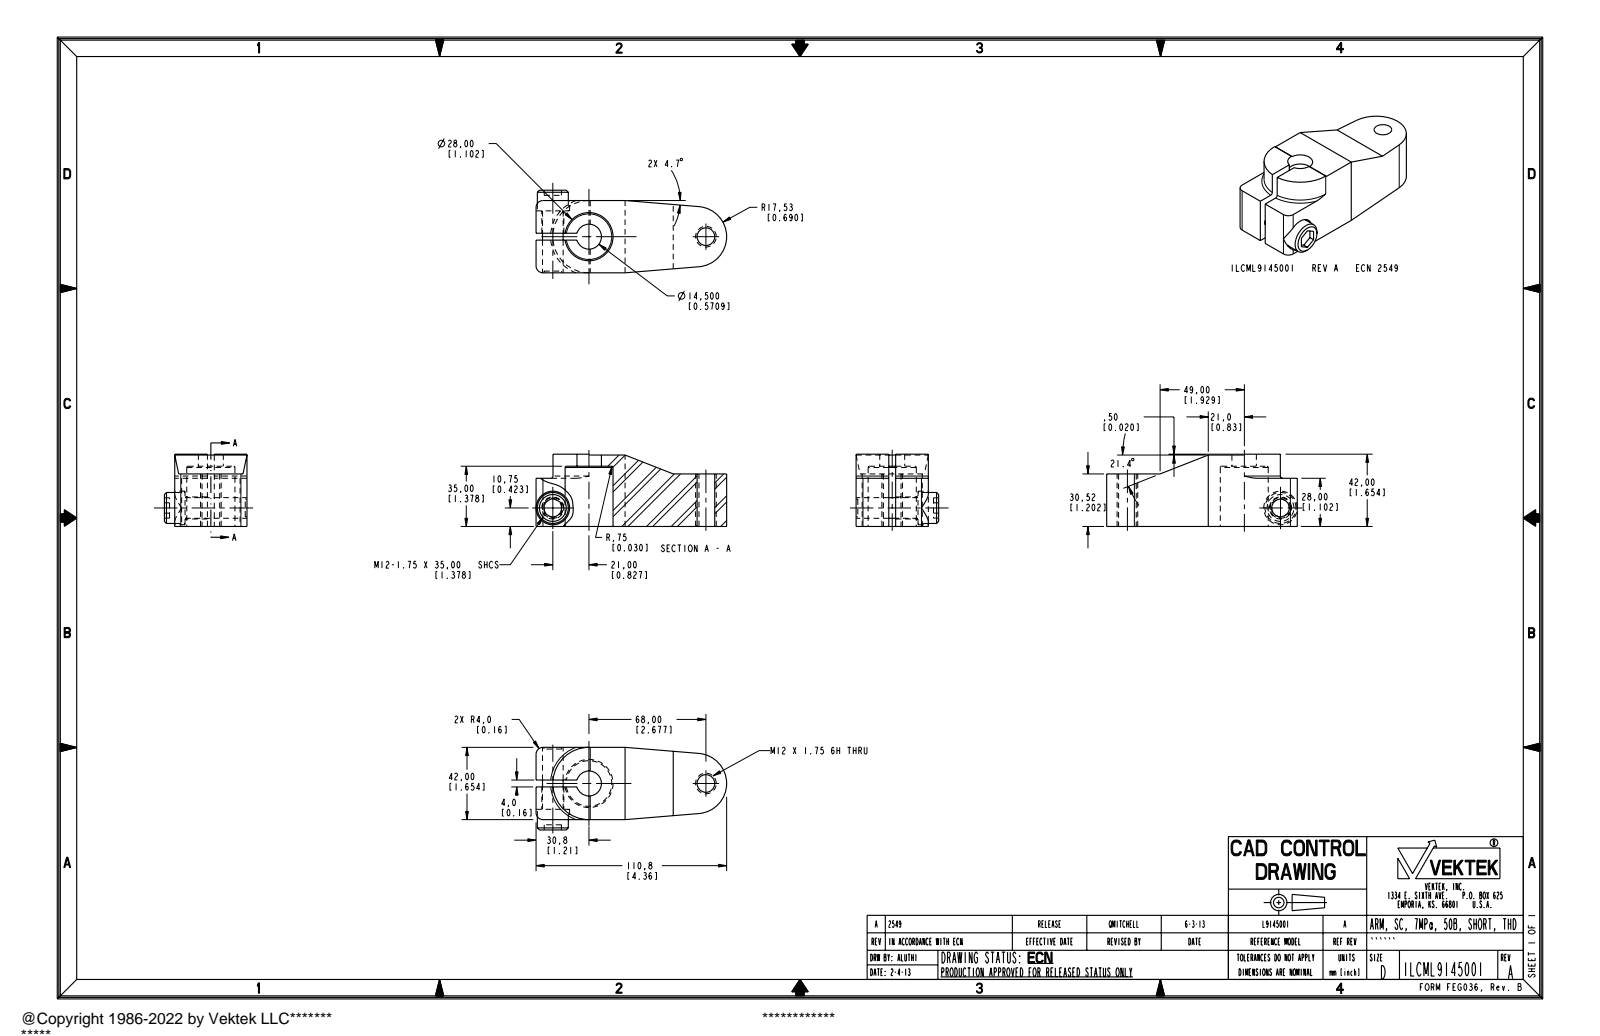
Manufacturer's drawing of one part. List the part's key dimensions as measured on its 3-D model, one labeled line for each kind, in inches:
Part name (STEP PRODUCT): ILCML9145001
STEP written by: PRO/ENGINEER BY PARAMETRIC TECHNOLOGY CORPORATION, 2007460 (AUTOMOTIVE_DESIGN_CC2)
Units: inches
Bodies: 1 solid, 59 faces (28 planar, 26 cylindrical, 5 other)
Overall size (bounding box): 4.362 × 1.89 × 1.654
Volume: 7.668 in³ · Surface area: 41.9 in²
Round holes (diameter × count): ⌀0.404 ×2, ⌀0.504 ×1, ⌀0.571 ×1, ⌀0.768 ×1, ⌀1.102 ×1
Round bosses / shafts (diameter × count): ⌀0.472 ×2, ⌀0.709 ×1
Partial cylindrical surfaces — rounded edges, fillets, slot ends (radius × count): R0.157 ×2, R0.031 ×1, R0.69 ×1, R0.827 ×1
Main face-to-face distances: 1.654, 0.748, 0.906, 1.202, 1.634, 0.432, 0.276, 0.452, 0.02, 0.157
Hole centre spacings: 2.677
